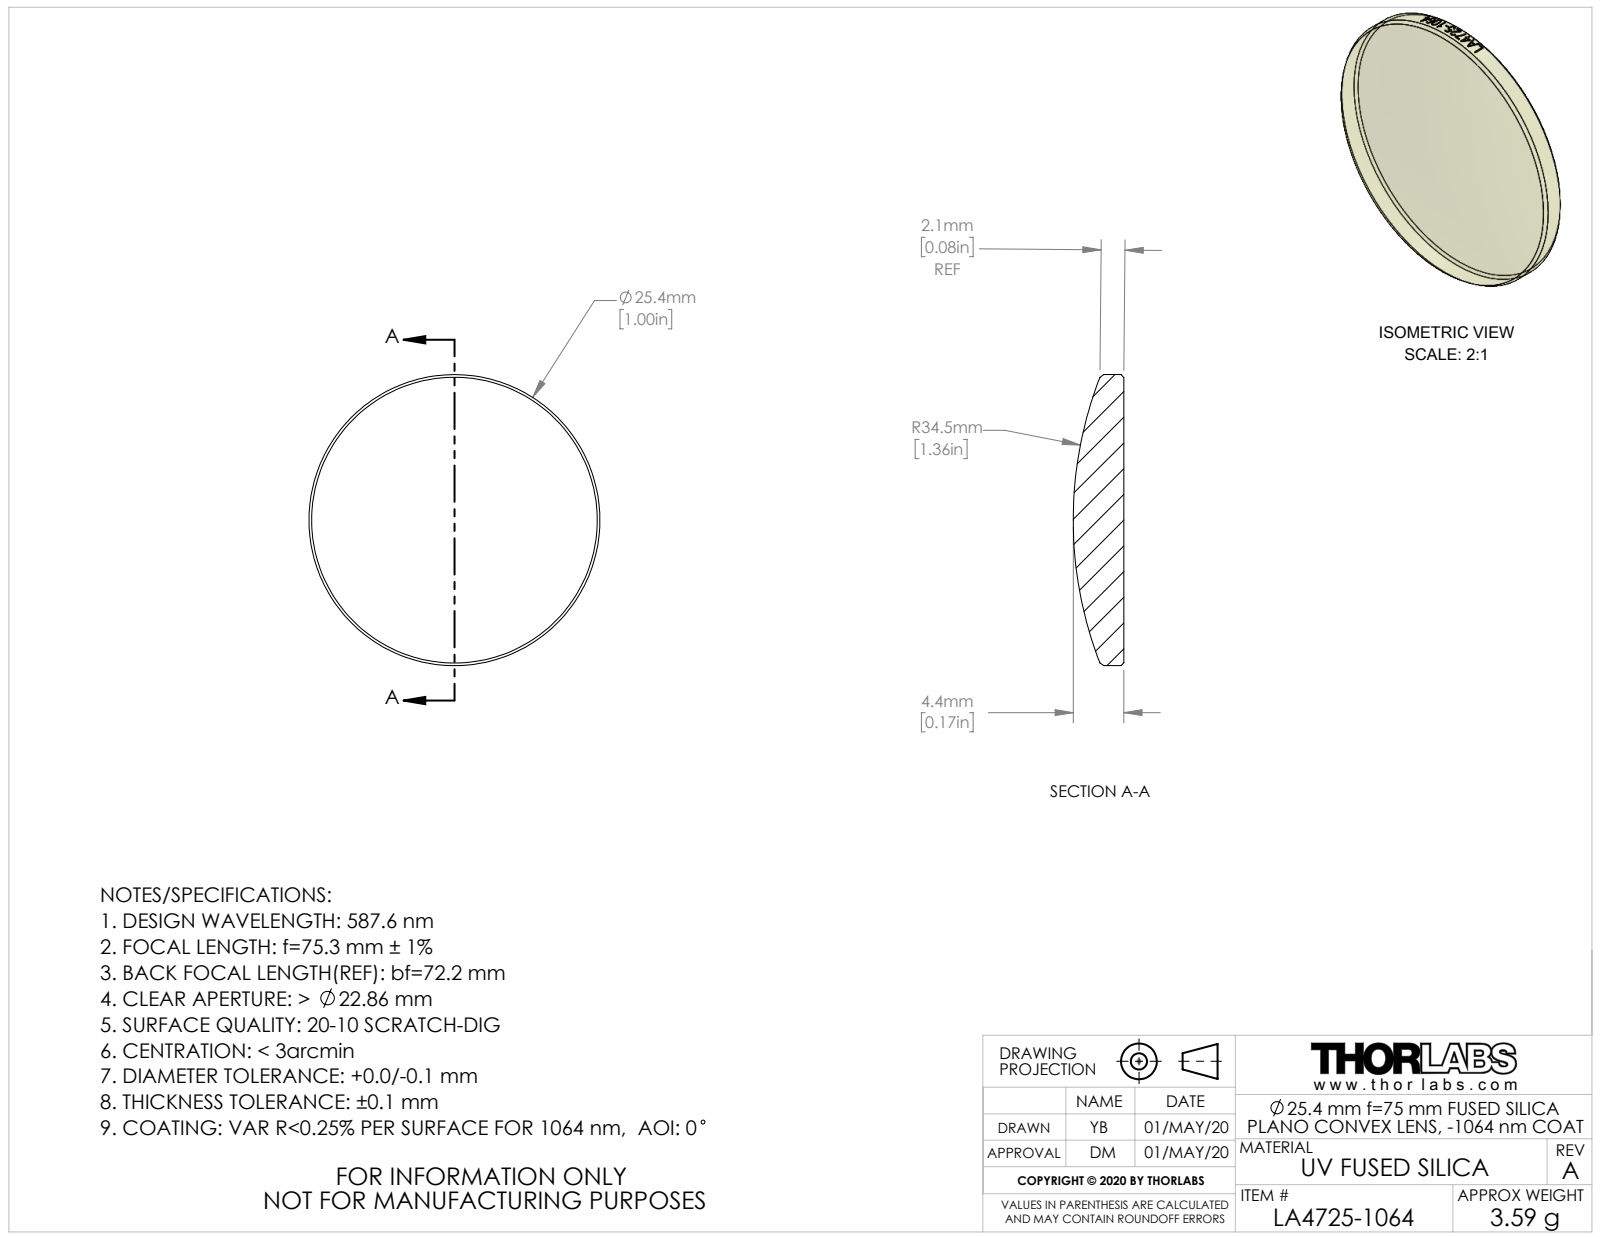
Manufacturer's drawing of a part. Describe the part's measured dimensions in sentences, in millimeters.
The part is named "CTN015555-E0W". Its 3-D file was written by "SolidWorks 2018 (AUTOMOTIVE_DESIGN)". It is 1 solid with 28 faces: 1 planar, 21 cylindrical and 6 other. Overall it measures 25.4 by 25.4 by 4.42 millimeters. Its volume is 1 629 cubic millimeters and its surface area 1 173 square millimeters. Round bosses or shafts: 1 of diameter 25.4.
